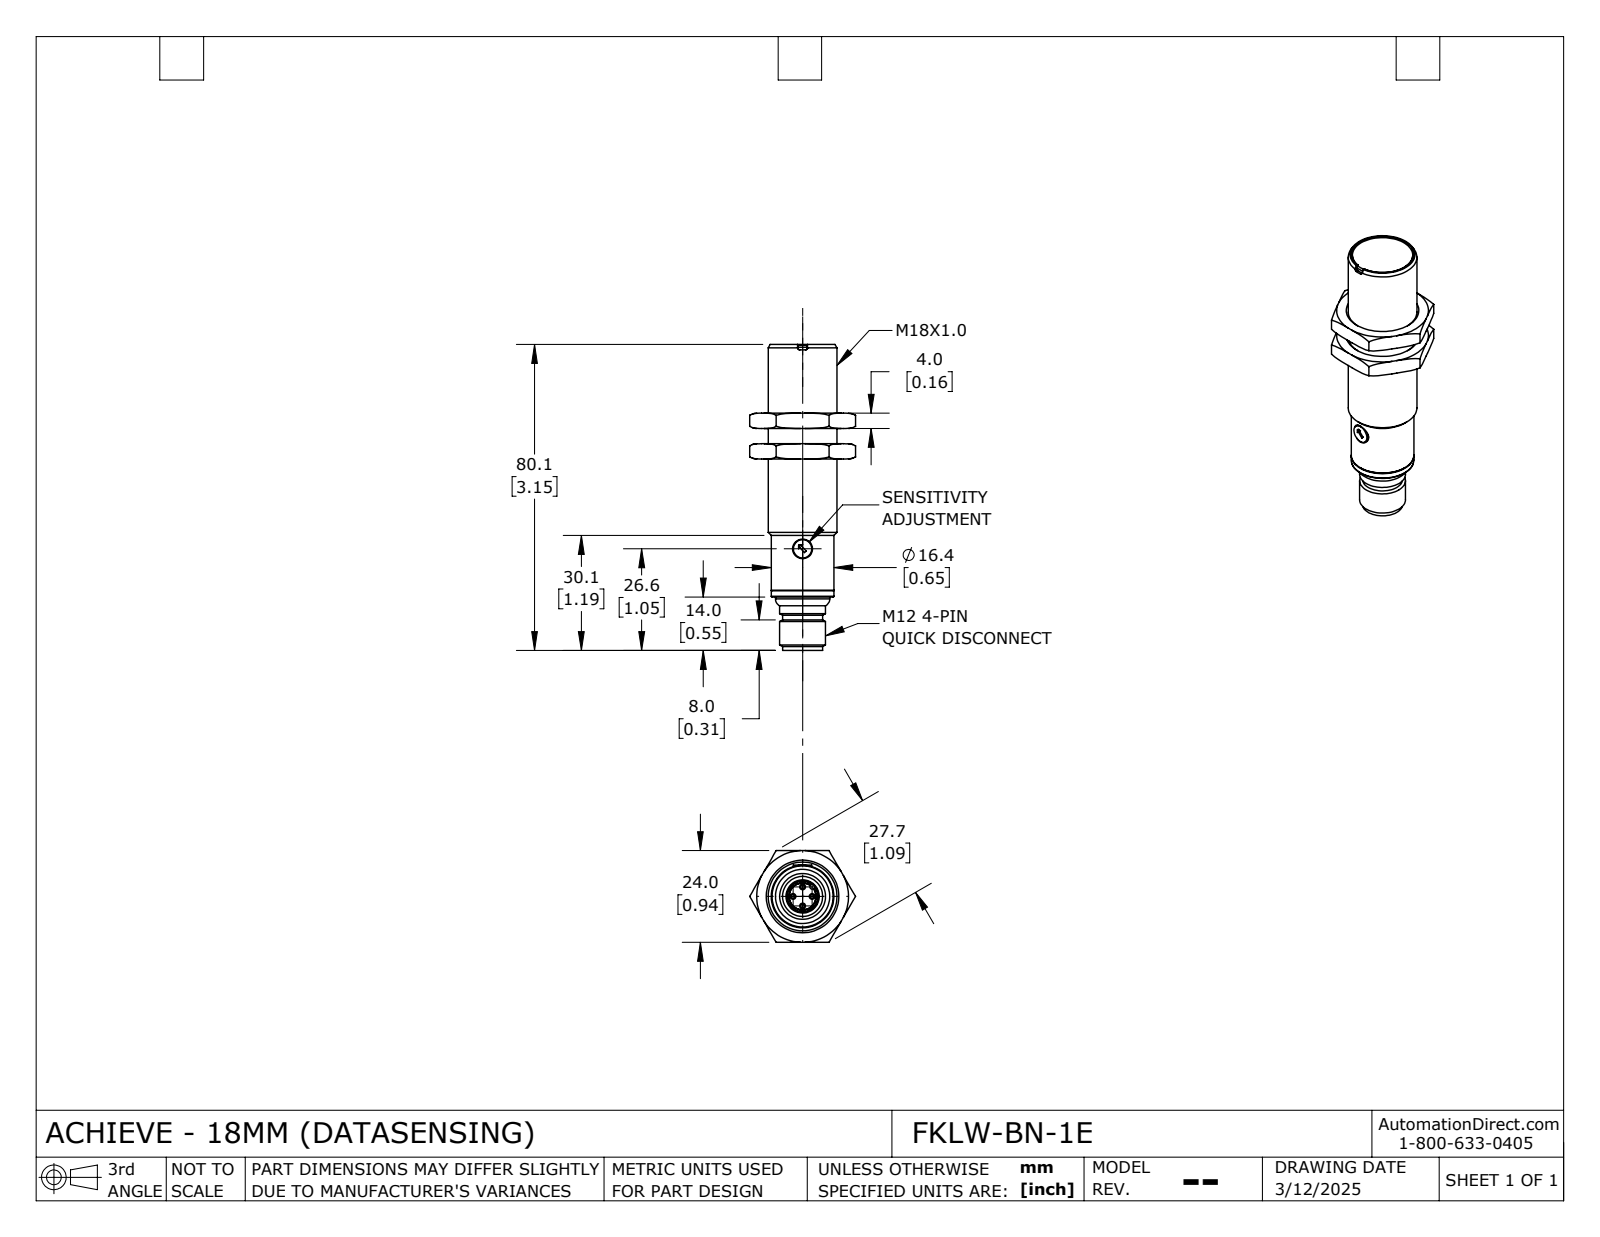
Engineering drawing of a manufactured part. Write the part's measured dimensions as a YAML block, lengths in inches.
part_name: "FKLW-BN-1E_Default"
step_written_by: "SolidWorks 2024 (CONFIG_CONTROL_DESIGN)"
units: inches
bodies: {solids: 4, faces: 135, planar: 54, cylindrical: 29, other: 52}
overall_size: [3.154, 1.091, 0.945]
volume: 1.259
surface_area: 12.98
round_holes:
  - {diameter: 0.106, count: 1}
  - {diameter: 0.185, count: 1}
  - {diameter: 0.278, count: 1}
  - {diameter: 0.327, count: 1}
  - {diameter: 0.622, count: 1}
  - {diameter: 0.709, count: 1}
round_bosses_or_shafts:
  - {diameter: 0.039, count: 4}
  - {diameter: 0.646, count: 1}
  - {diameter: 0.559, count: 1}
  - {diameter: 0.472, count: 1}
  - {diameter: 0.413, count: 1}
  - {diameter: 0.276, count: 1}
  - {diameter: 0.189, count: 1}
partial_cylinders:
  - {radius: 0.02, count: 4}
  - {radius: 0.024, count: 1}
  - {radius: 0.331, count: 1}
face_to_face_distances: [0.157, 0.315, 0.945, 0.472, 0.055, 0.348, 0.403, 0.612, 0.96, 1.015]
